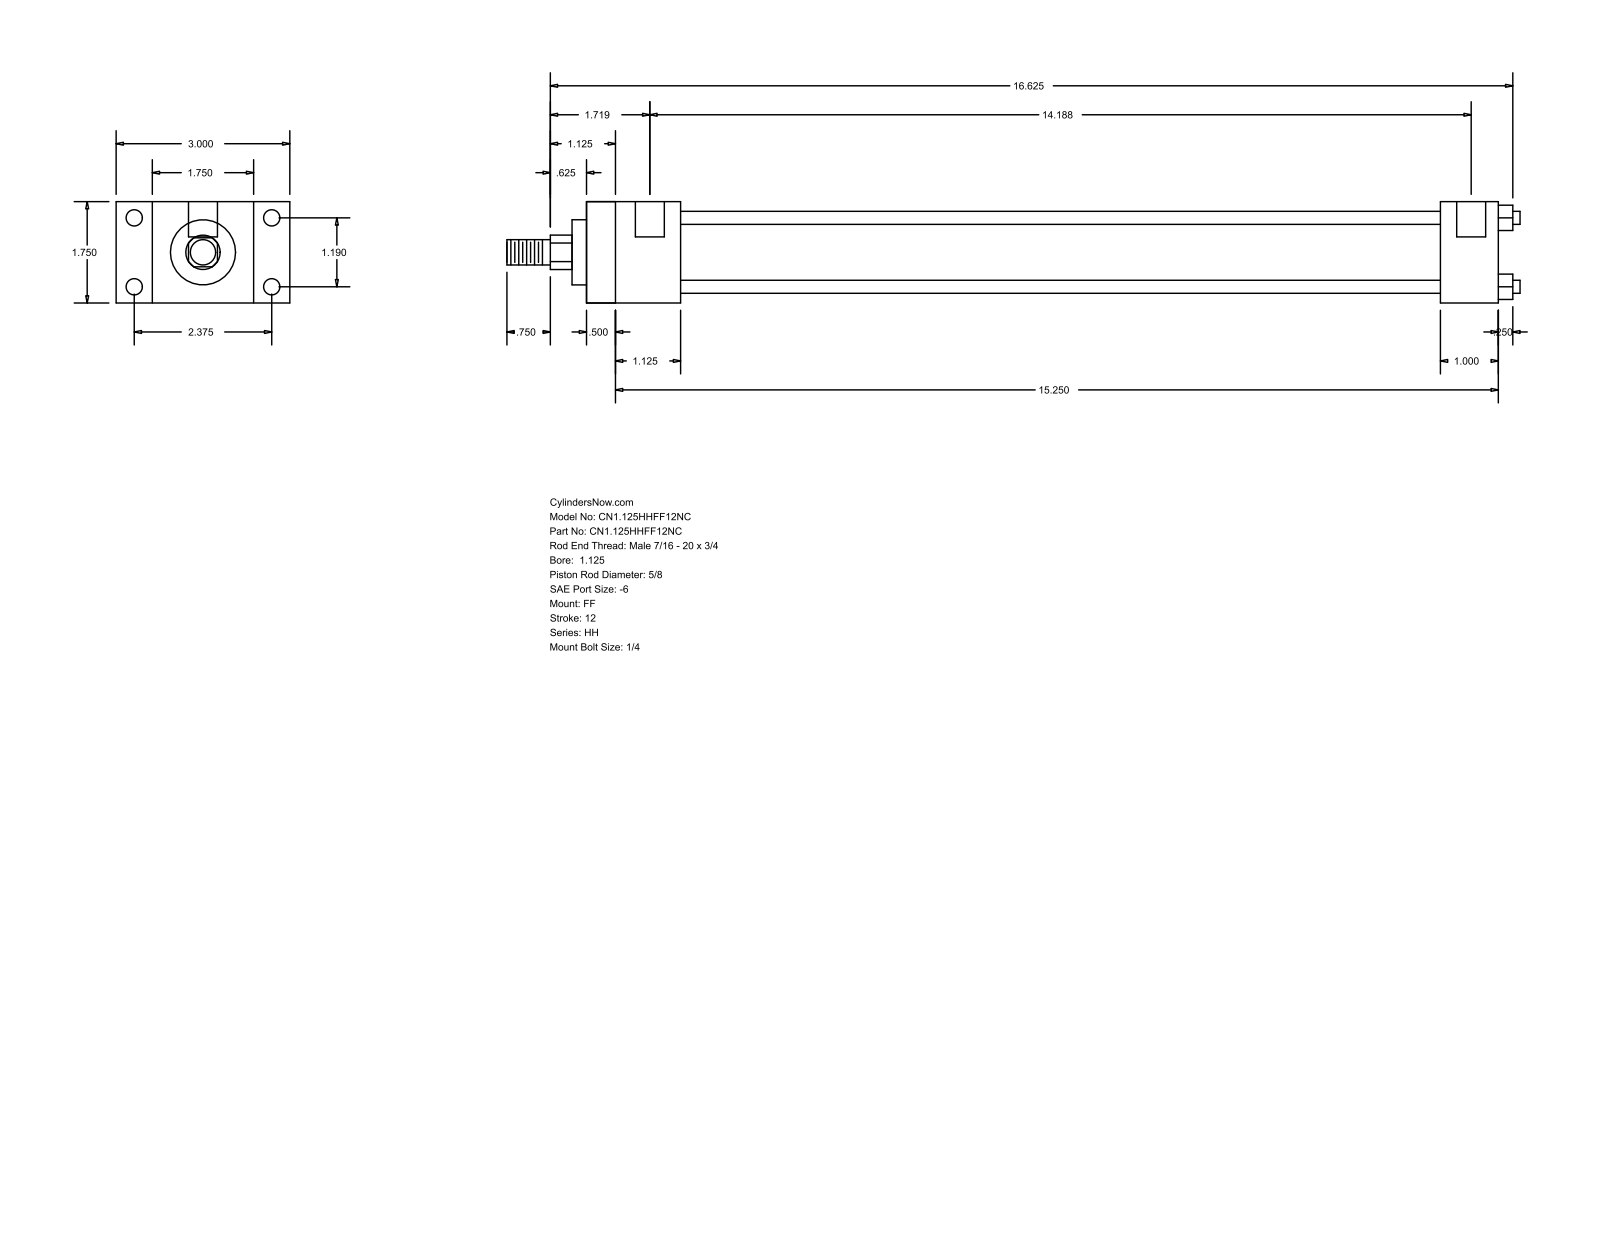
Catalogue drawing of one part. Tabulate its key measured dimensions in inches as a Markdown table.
| quantity | value |
| --- | --- |
| part name | HH_FF__0112_0.625 |
| STEP written by | GSSL Pune (CONFIG_CONTROL_DESIGN) |
| units | inches |
| bodies | 0 solids, 92 faces (64 planar, 28 cylindrical, 0 other) |
| overall size | 17.5 × 3 × 1.75 |
| round holes (diameter × count) | 0.219 × 4, 0.281 × 4, 0.5 × 2 |
| round bosses / shafts (diameter × count) | 0.225 × 4, 1.375 × 1, 1.125 × 1, 0.625 × 1, 0.437 × 1 |
| partial cylindrical surfaces (radius × count) | 0.297 × 1 |
| main face-to-face distances | 1.75, 15.75, 0.625, 0.5, 15.25, 1.125, 2.375, 1.625, 14.75, 14.25 |
| hole center spacings | 1.19, 2.375, 2.656, 14.063, 0.125, 14.187 |
